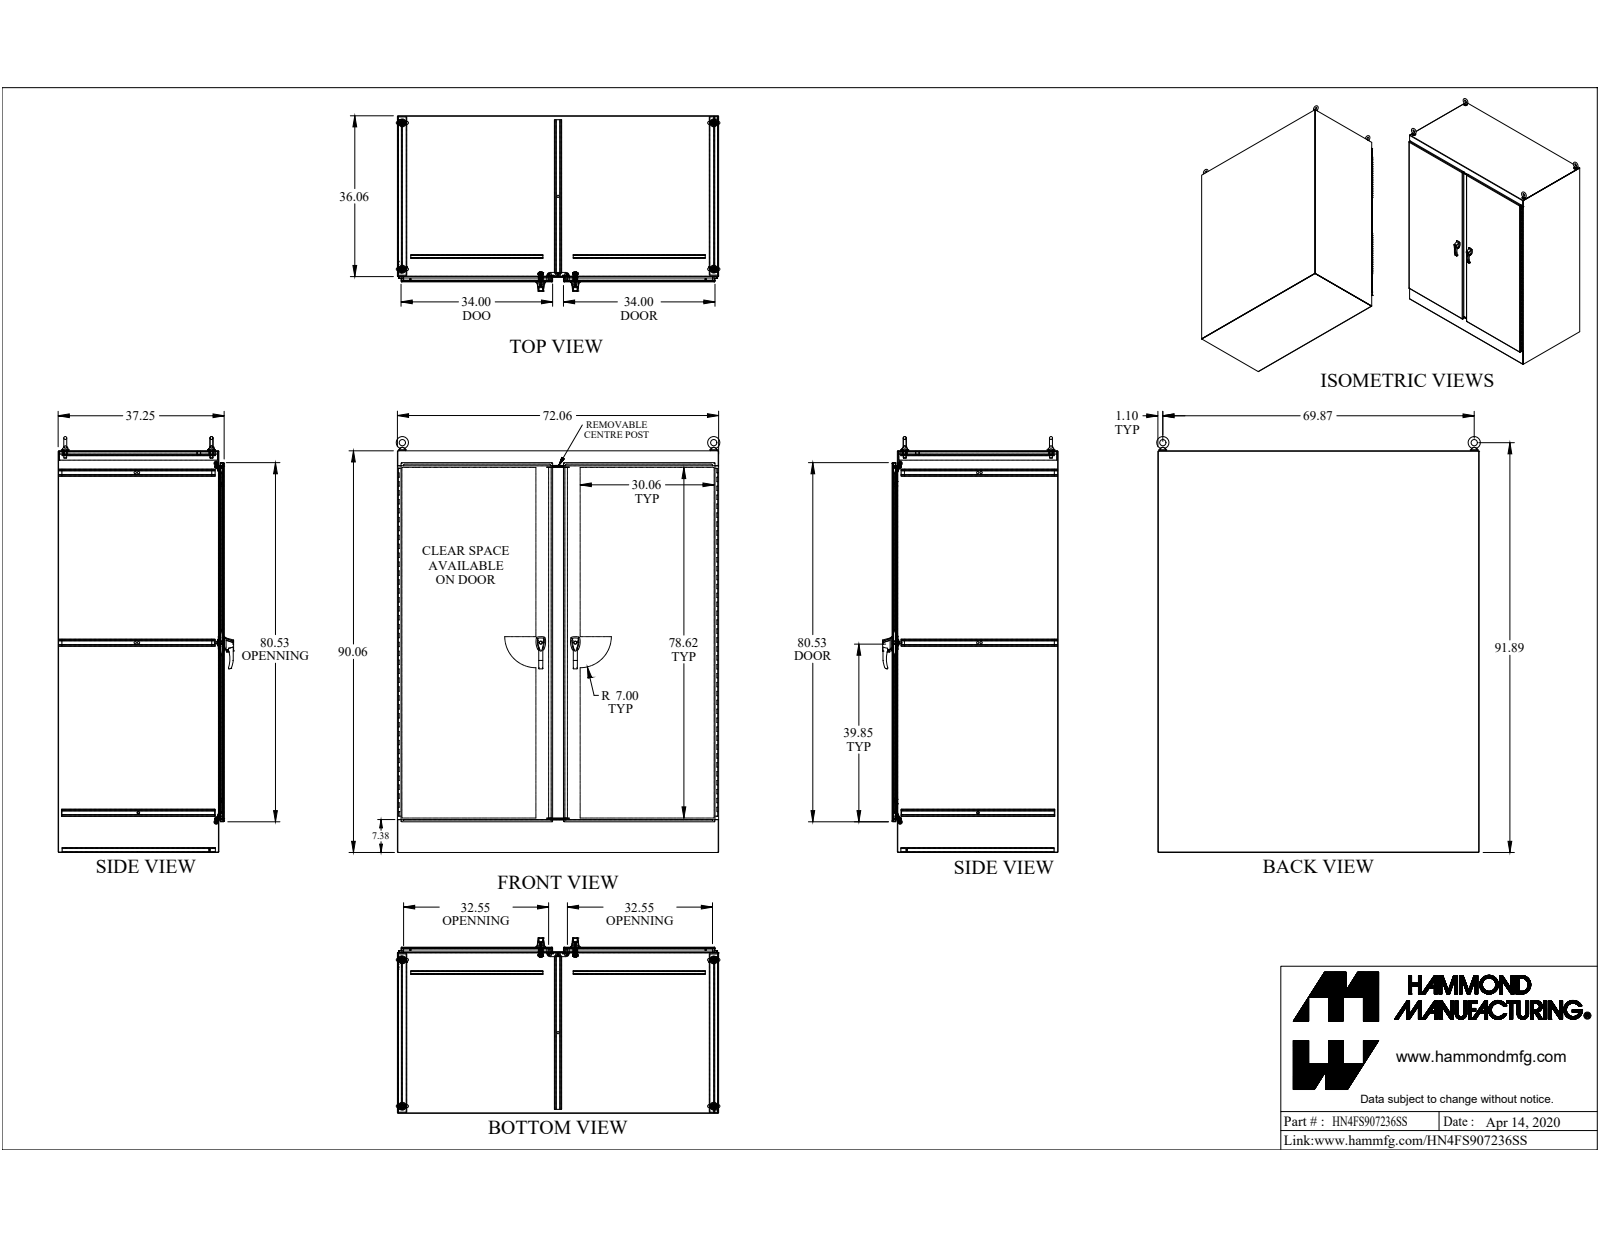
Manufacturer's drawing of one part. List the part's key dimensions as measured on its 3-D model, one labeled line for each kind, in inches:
Part name (STEP PRODUCT): HN4FS907236SS
STEP written by: SolidWorks 2019 (CONFIG_CONTROL_DESIGN)
Units: inches
Bodies: 115 solids, 3237 faces (1697 planar, 1280 cylindrical, 260 other)
Overall size (bounding box): 93.256 × 72.604 × 39.362
Volume: 2 741 in³ · Surface area: 57 986 in²
Round holes (diameter × count): ⌀0.304 ×26, ⌀0.35 ×8, ⌀0.5 ×7, ⌀0.75 ×6, ⌀0.25 ×5, ⌀0.281 ×4, ⌀0.313 ×4, ⌀0.39 ×4, ⌀0.527 ×4, ⌀0.625 ×4, ⌀0.68 ×4, ⌀0.201 ×3
Round bosses / shafts (diameter × count): ⌀1.75 ×4, ⌀1.5 ×4, ⌀1.25 ×4, ⌀0.75 ×4, ⌀0.625 ×4, ⌀0.624 ×4, ⌀0.44 ×4, ⌀0.37 ×4
Partial cylindrical surfaces — rounded edges, fillets, slot ends (radius × count): R0.043 ×54, R0.138 ×48, R0.5 ×33, R0.018 ×32, R0.06 ×24, R0.125 ×23, R0.1 ×22, R0.036 ×14
Main face-to-face distances: 0.095, 37.152, 71.965, 37.057, 37.247, 89.965, 71.87, 72.06, 89.87, 90.06
Hole centre spacings: 6, 70.584, 12, 71.345, 18, 72.595, 24, 74.311
